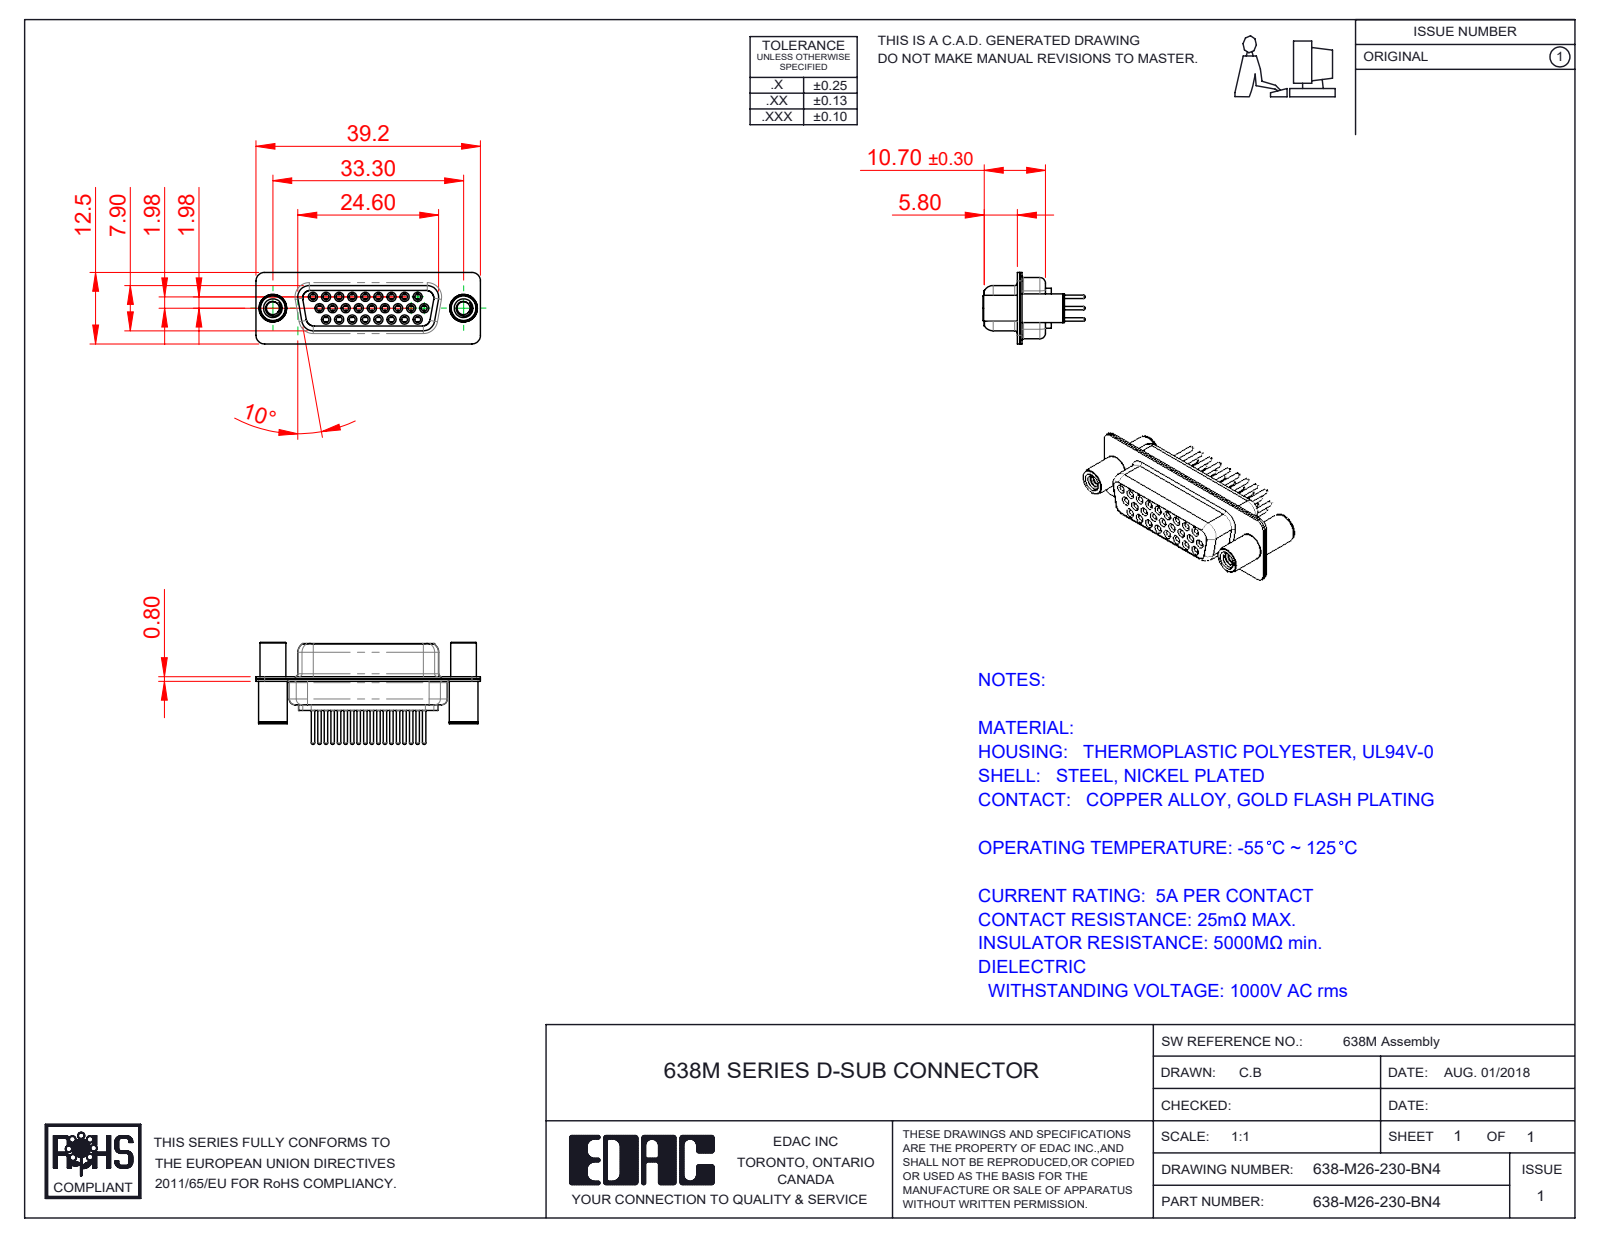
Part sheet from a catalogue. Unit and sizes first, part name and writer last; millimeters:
Units: millimetres
Overall size (bounding box): 39.2 × 17.8 × 12.5
Round holes (diameter × count): ⌀1 ×26, ⌀1.1 ×26, ⌀1.7 ×26, ⌀1.8 ×26, ⌀2 ×26, ⌀2.26 ×2, ⌀3.26 ×2, ⌀4 ×2, ⌀4.8 ×2
Round bosses / shafts (diameter × count): ⌀2.2 ×26, ⌀1.6 ×26, ⌀1.5 ×26, ⌀0.6 ×26, ⌀5 ×2, ⌀4.9 ×2, ⌀4.5 ×2
Partial cylindrical surfaces — rounded edges, fillets, slot ends (radius × count): R1.5 ×16, R2 ×12, R1.35 ×8, R1.6 ×8, R0.25 ×4, R0.5 ×4, R0.6 ×4, R0.65 ×4
Main face-to-face distances: 0.4, 1.4, 0.45, 8.45, 8.9, 1.8, 1, 6.2, 7.05, 1.85
Hole centre spacings: 3.96, 2.28, 4.57, 6.05, 2.29, 8.24, 6.86, 6.04
Volume: 2 640 mm³ · Surface area: 8 391 mm²
Bodies: 31 solids, 1795 faces (463 planar, 683 cylindrical, 649 other)
Part name (STEP PRODUCT): 638-M26-230-BN4; 638M 4-40 Threaded Standoff and Board Spacer; 638M Contact Row 2_30; 638M Contact Row 3_30 (+4 more)
STEP written by: SolidWorks 2020 (CONFIG_CONTROL_DESIGN)
